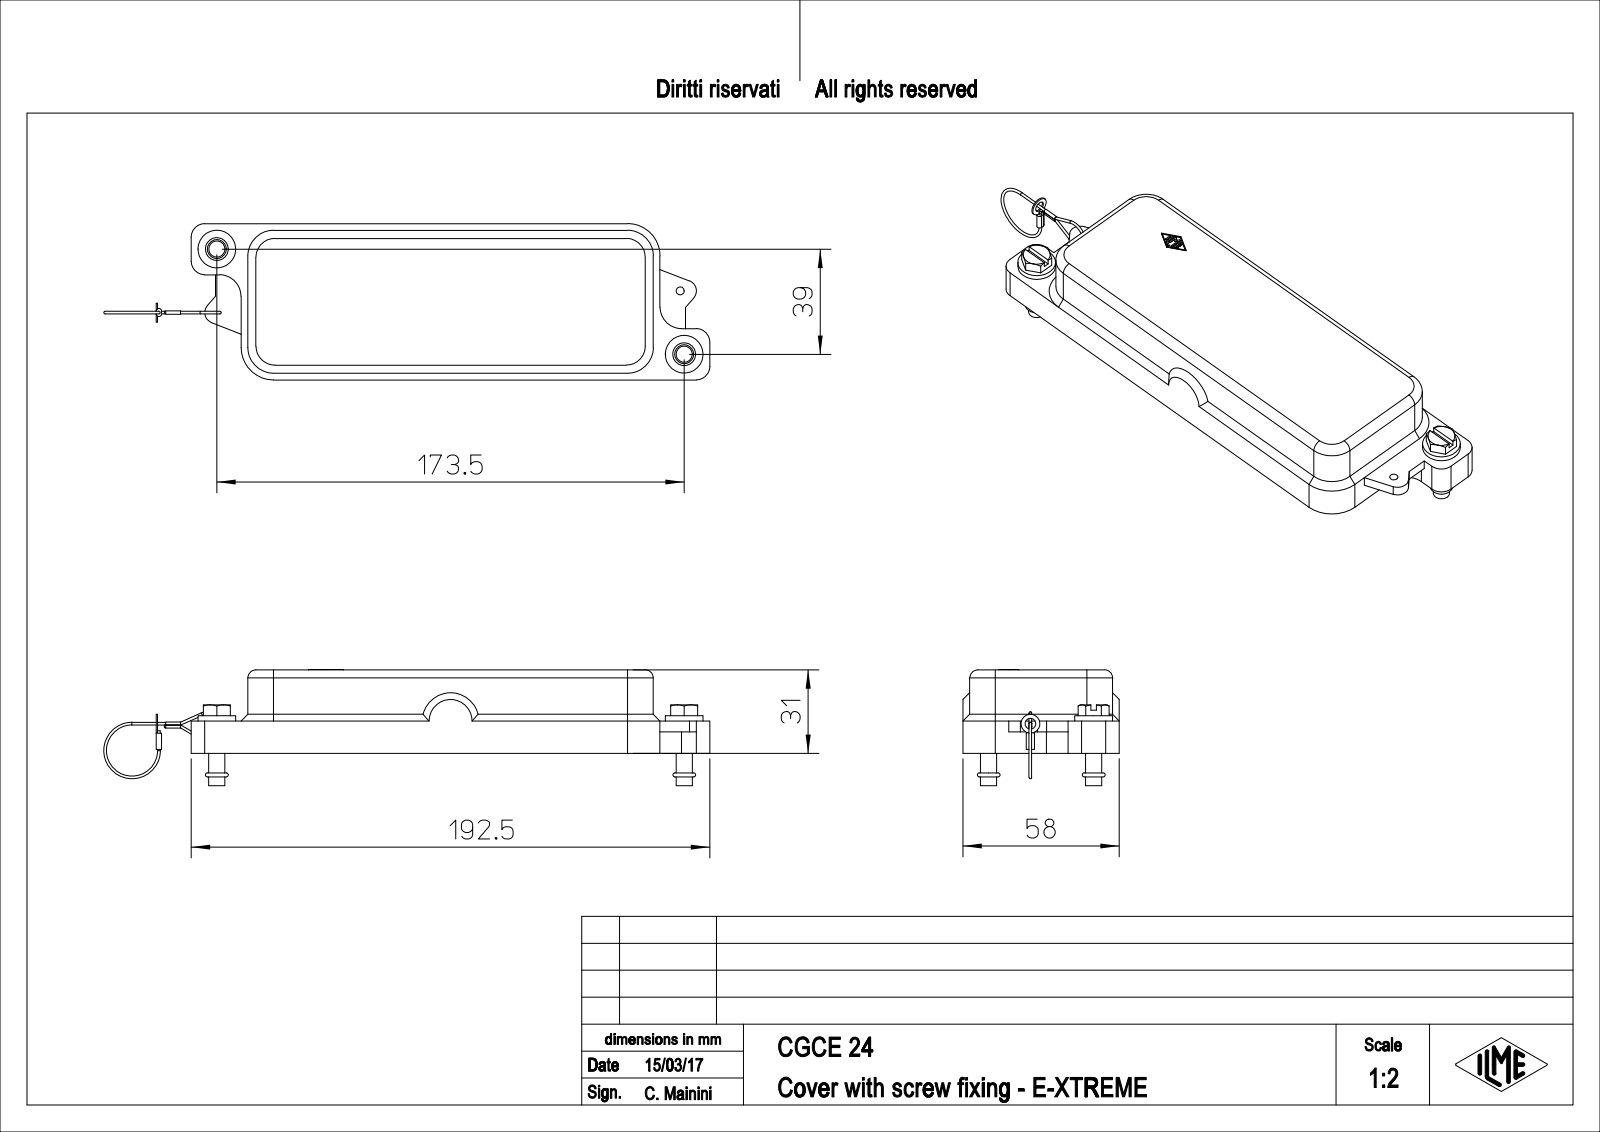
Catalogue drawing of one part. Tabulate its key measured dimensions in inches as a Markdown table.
| quantity | value |
| --- | --- |
| part name | CGCE_24 |
| STEP written by | PTC Creo Elements/Direct Modeling 19.0E 27-Jun-2016 (C) Parametric Technology GmbH (AUTOMOTIVE_DESIGN) |
| units | inches |
| bodies | 1 solid, 247 faces (124 planar, 87 cylindrical, 36 other) |
| overall size | 8.858 × 2.283 × 1.697 |
| volume | 5.874 in³ |
| surface area | 68.77 in² |
| round holes (diameter × count) | 0.276 × 2, 0.551 × 2, 0.118 × 1, 0.157 × 1 |
| round bosses / shafts (diameter × count) | 0.039 × 5, 0.236 × 2, 0.217 × 2, 0.276 × 1 |
| partial cylindrical surfaces (radius × count) | 0.01 × 14, 0.118 × 4, 0.197 × 4, 0.276 × 4, 0.374 × 4, 0.024 × 2, 0.039 × 2, 0.157 × 2 |
| main face-to-face distances | 0.276, 0.118, 0.098, 0.217, 2.185, 2.067, 1.969, 2.087, 1.85, 2.283 |
| hole center spacings | 0.927, 6.799, 7.001 |
